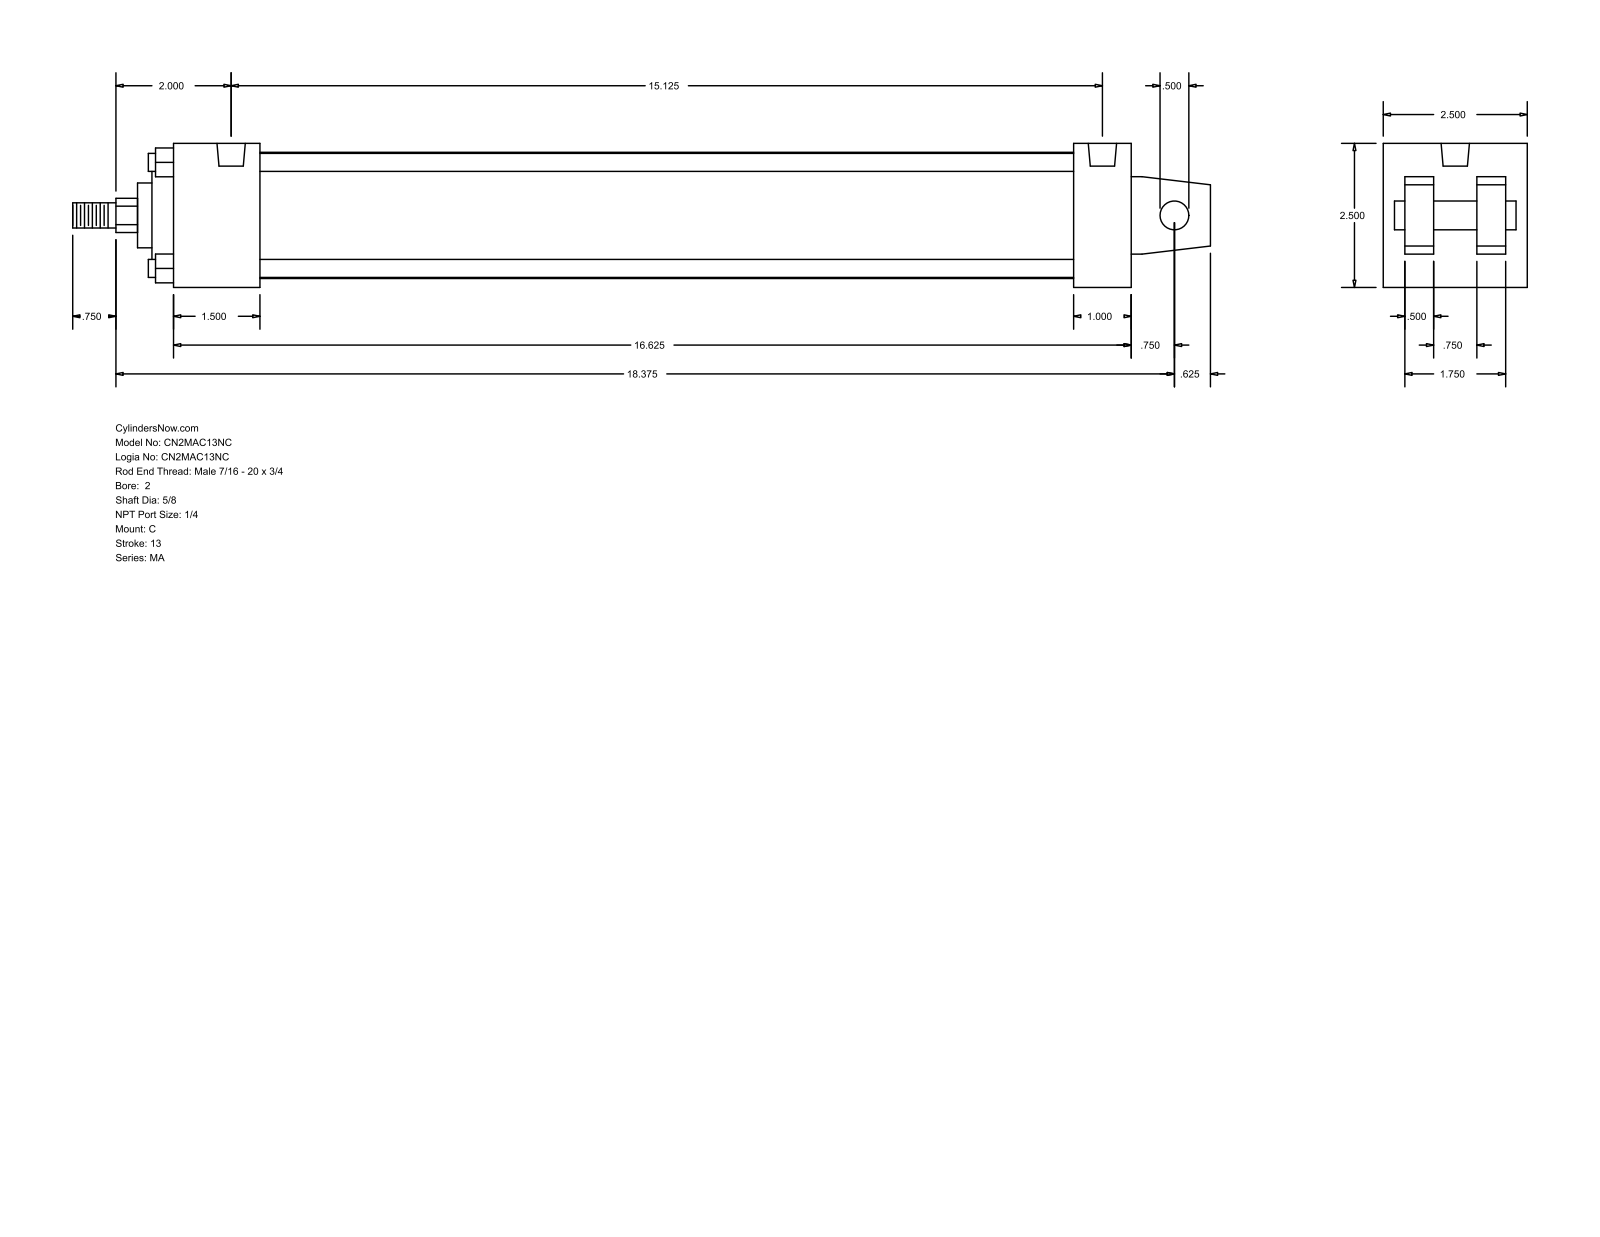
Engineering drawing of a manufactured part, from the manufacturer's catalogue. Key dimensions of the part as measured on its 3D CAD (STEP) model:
Part name (STEP PRODUCT): MA_C__0200_0.625
STEP written by: GSSL Pune (CONFIG_CONTROL_DESIGN)
Units: millimetres
Bodies: 0 solids, 105 faces (77 planar, 28 cylindrical, 0 other)
Overall size (bounding box): 501.65 × 63.5 × 63.5
Round holes (diameter × count): ⌀7.94 ×4, ⌀12.49 ×2
Round bosses / shafts (diameter × count): ⌀7.94 ×4, ⌀55.63 ×1, ⌀50.8 ×1, ⌀28.57 ×1, ⌀15.88 ×1, ⌀12.7 ×1, ⌀11.11 ×1
Partial cylindrical surfaces — rounded edges, fillets, slot ends (radius × count): R7.54 ×1
Main face-to-face distances: 63.5, 9.52, 12.7, 22.22, 41.28, 53.98, 31.76, 38.1, 422.28, 384.18
Hole centre spacings: 384.18
